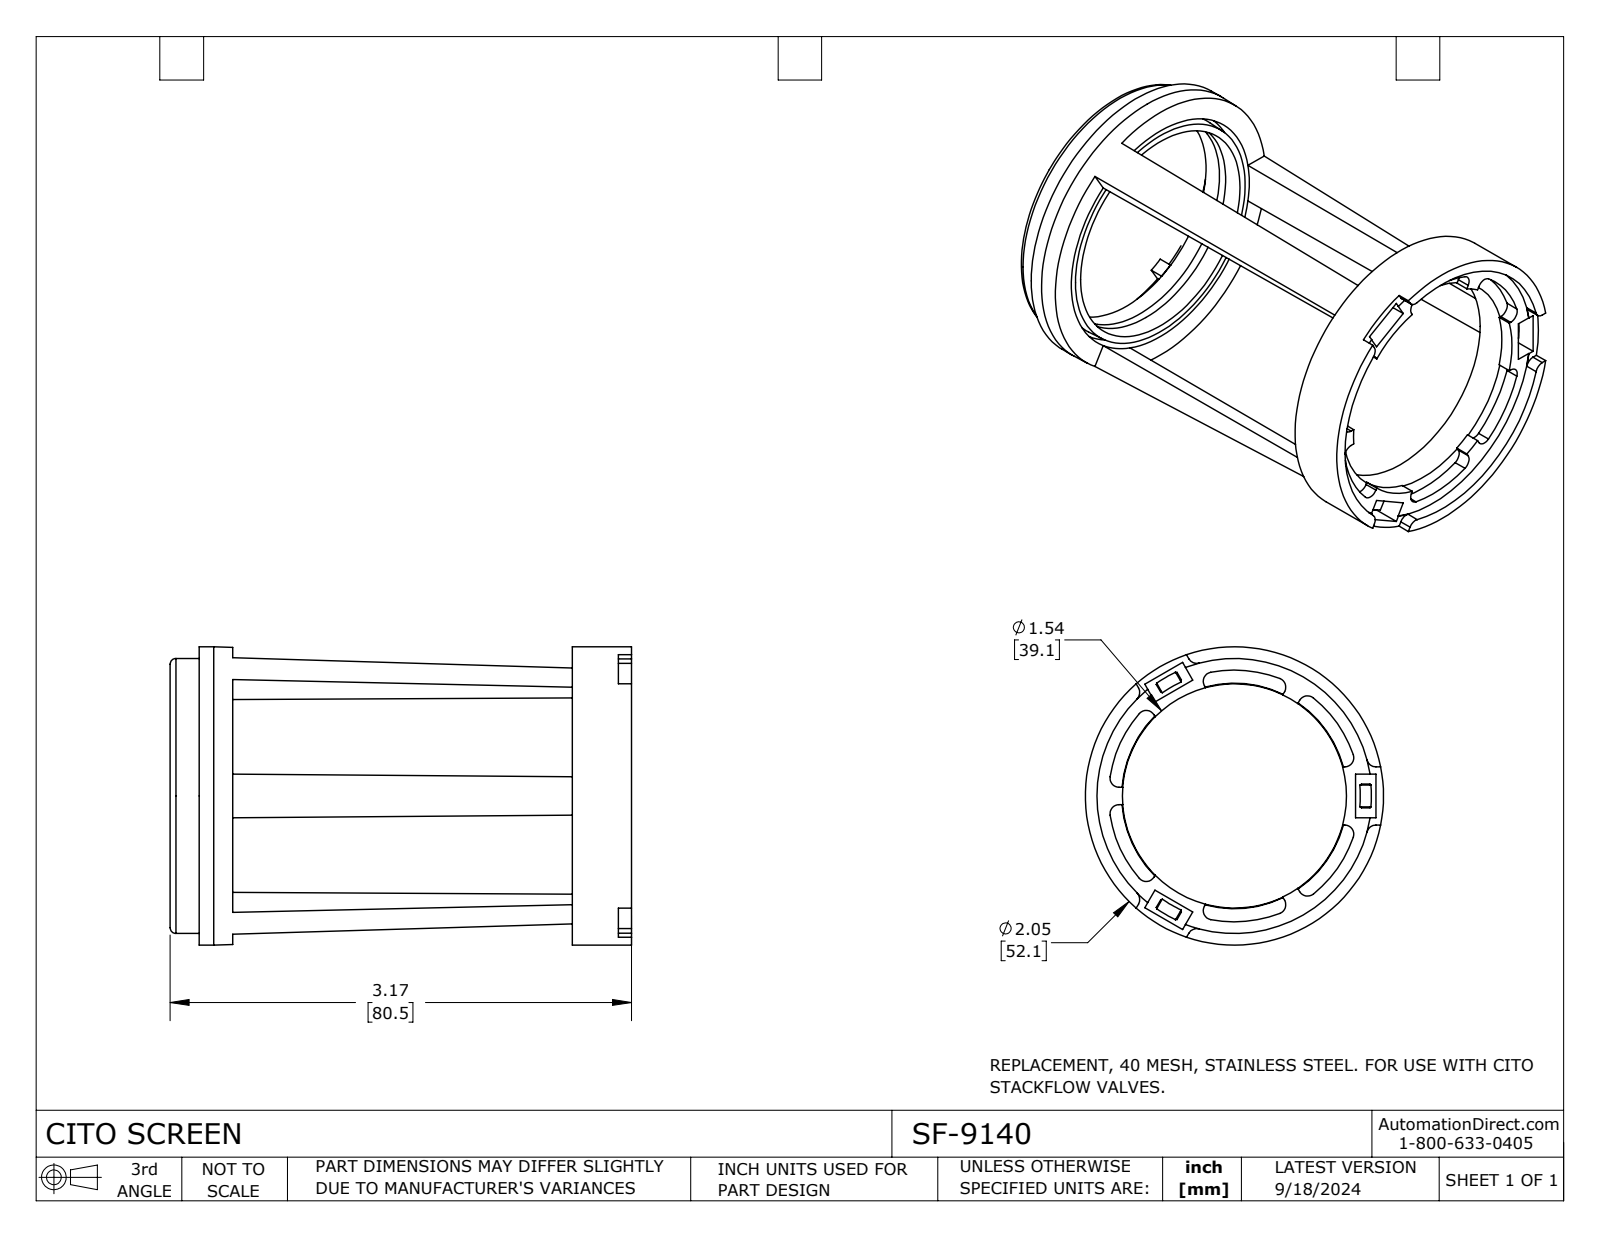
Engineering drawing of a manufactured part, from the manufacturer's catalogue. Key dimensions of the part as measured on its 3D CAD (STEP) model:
Part name (STEP PRODUCT): SF-9140
STEP written by: SolidWorks 2023 (CONFIG_CONTROL_DESIGN)
Units: inches
Bodies: 2 solids, 191 faces (112 planar, 65 cylindrical, 14 other)
Overall size (bounding box): 3.171 × 2.05 × 2.05
Volume: 1.085 in³ · Surface area: 23.95 in²
Round holes (diameter × count): ⌀1.55 ×1, ⌀1.73 ×1, ⌀1.89 ×1
Round bosses / shafts (diameter × count): ⌀2.05 ×1, ⌀1.65 ×1
Partial cylindrical surfaces — rounded edges, fillets, slot ends (radius × count): R0.062 ×10, R0.063 ×8, R0.77 ×1, R0.771 ×1
Main face-to-face distances: 2.335, 0.1, 2.649, 0.314, 0.23, 2.565, 2.879, 2.979, 0.33, 2.665
